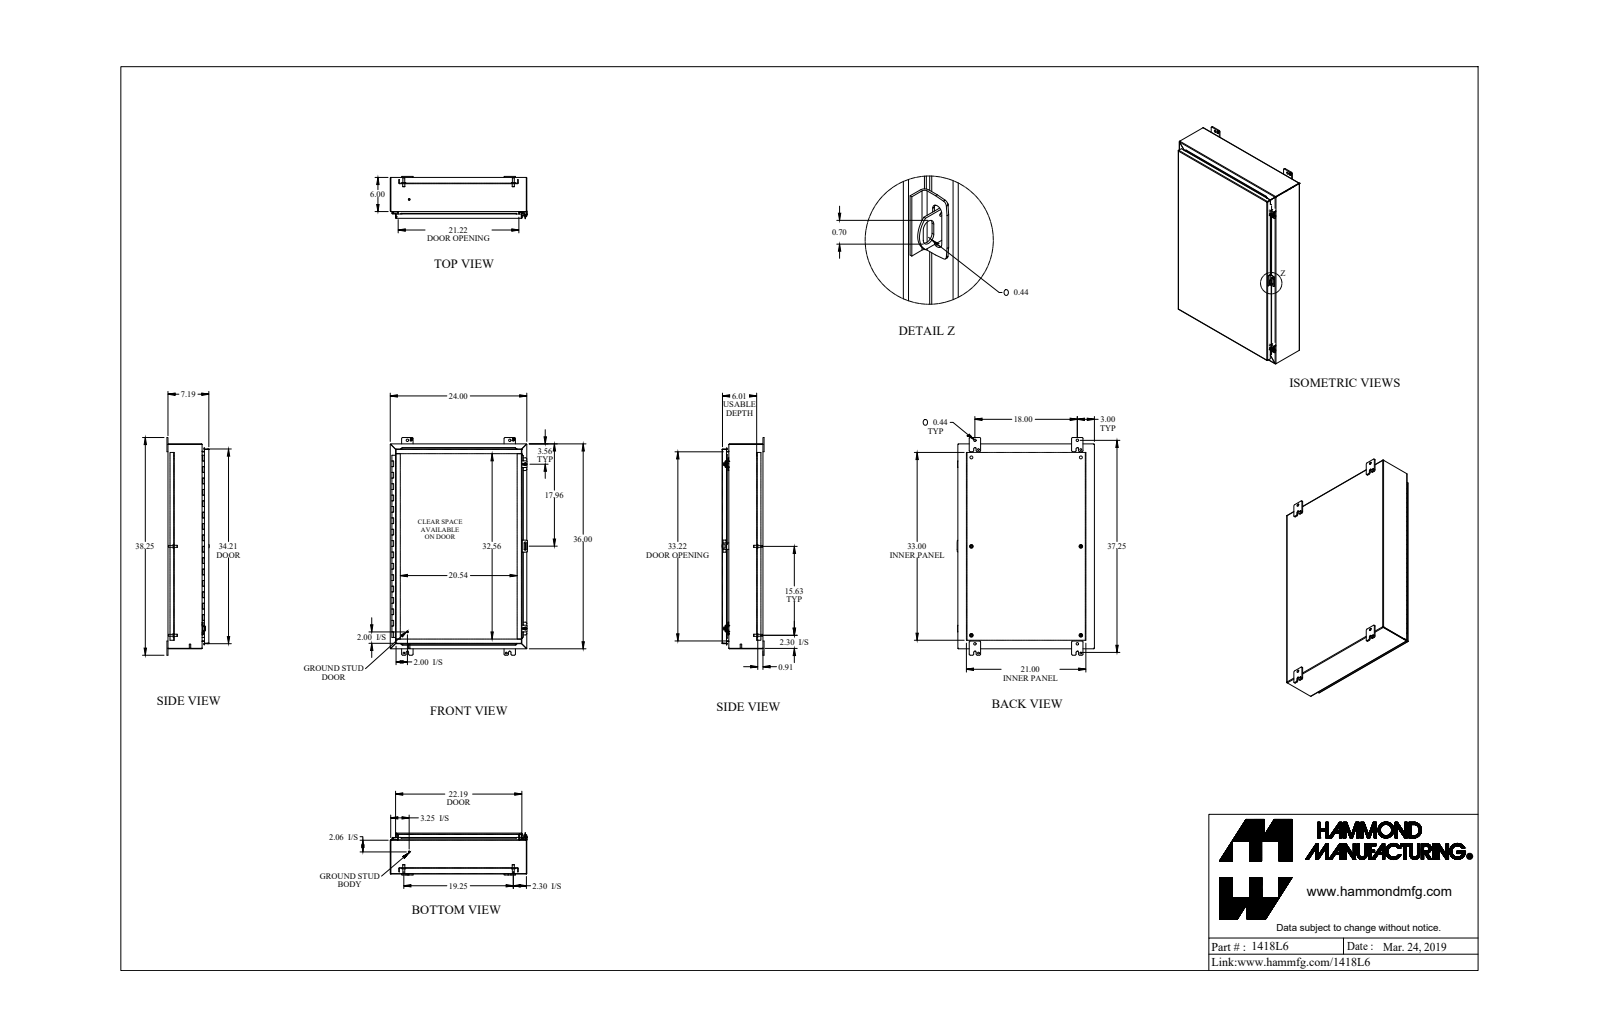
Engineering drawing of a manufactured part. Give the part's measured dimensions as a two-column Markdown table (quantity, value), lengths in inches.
| quantity | value |
| --- | --- |
| part name | 1418L6_Default |
| STEP written by | SolidWorks 2019 (CONFIG_CONTROL_DESIGN) |
| units | inches |
| bodies | 44 solids, 1334 faces (791 planar, 459 cylindrical, 84 other) |
| overall size | 38.25 × 24.125 × 7.437 |
| volume | 292 in³ |
| surface area | 7 513 in² |
| round holes (diameter × count) | 0.5 × 6, 0.307 × 4, 0.313 × 4, 0.437 × 4, 0.213 × 2, 0.265 × 2, 0.375 × 2, 0.445 × 2, 0.445 × 2, 0.125 × 1, 0.187 × 1 |
| round bosses / shafts (diameter × count) | 0.65 × 6, 0.375 × 6, 0.33 × 6, 1 × 4, 0.5 × 2, 0.39 × 2, 0.281 × 2, 0.25 × 2 |
| partial cylindrical surfaces (radius × count) | 0.188 × 26, 0.036 × 24, 0.108 × 24, 0.048 × 13, 0.143 × 13, 0.045 × 8, 0.218 × 8, 0.25 × 8 |
| main face-to-face distances | 0.072, 7.113, 7.041, 0.937, 7.185, 0.095, 1.009, 6.081, 6.009, 1.032 |
| hole center spacings | 19.25, 15.625, 18, 40.026, 2.434, 24.793, 24.793, 31.25 |
